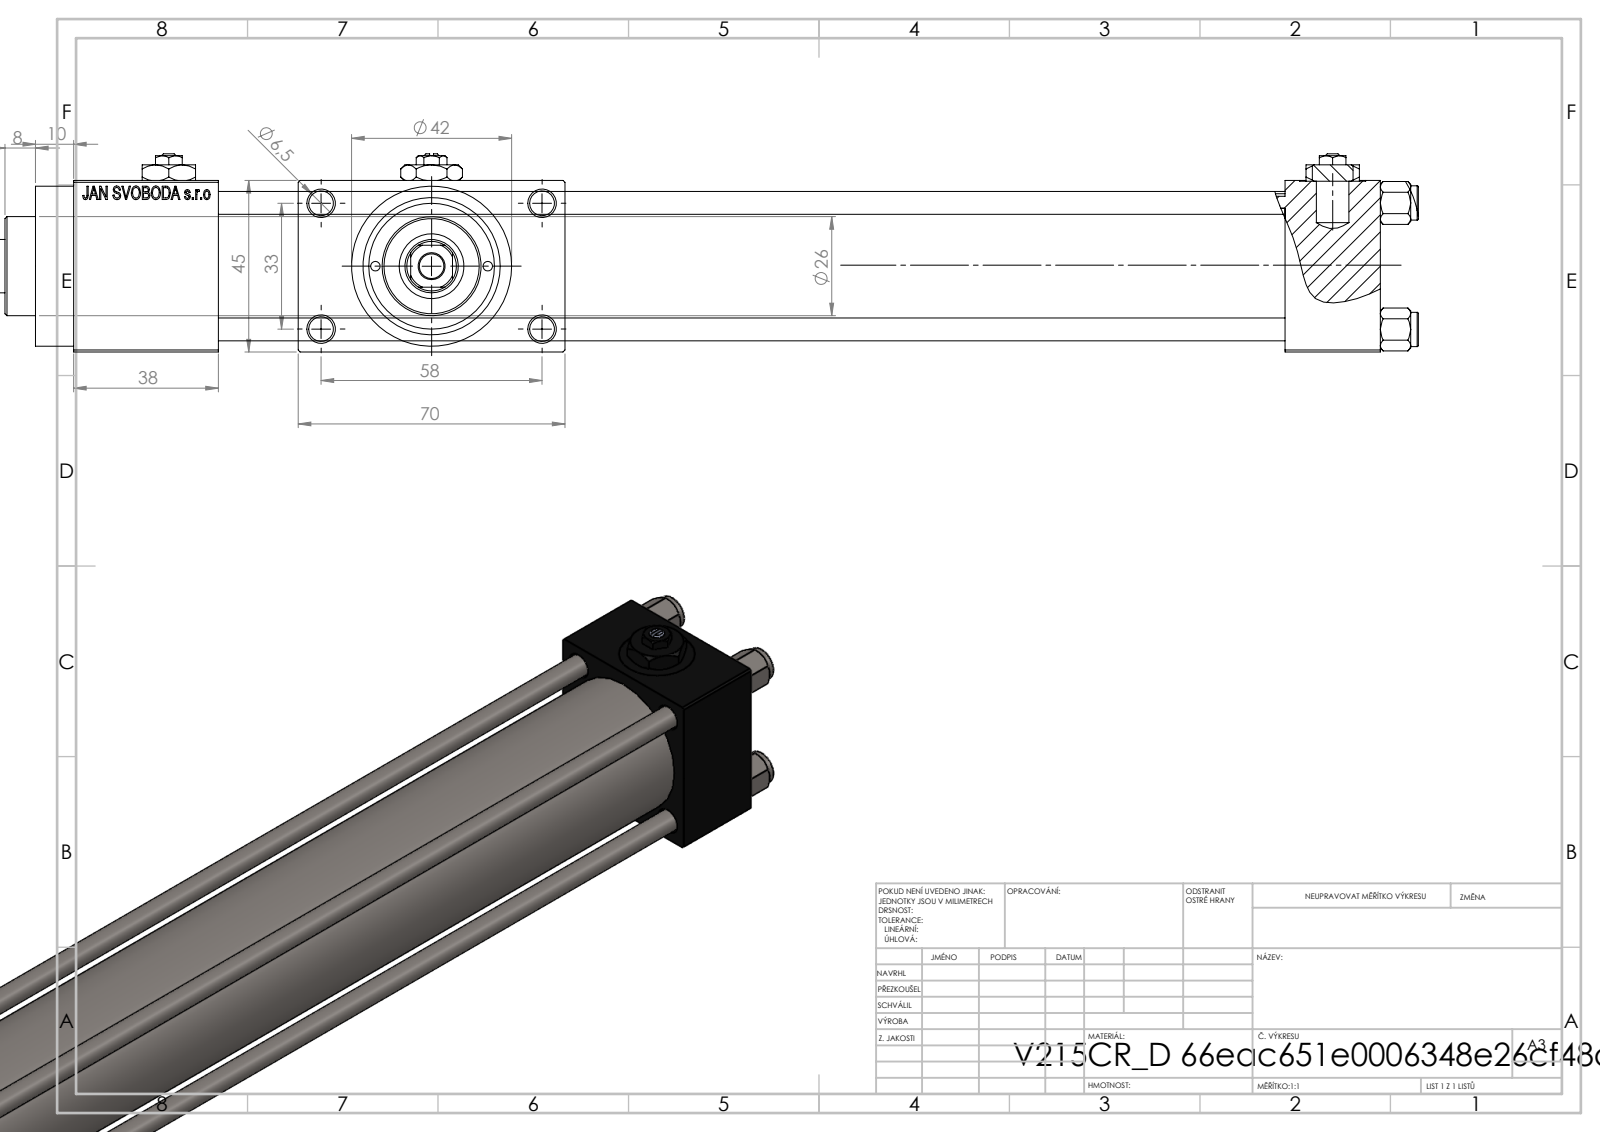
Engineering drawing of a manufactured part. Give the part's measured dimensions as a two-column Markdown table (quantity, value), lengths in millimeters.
| quantity | value |
| --- | --- |
| part name | V215CR_D_TYCINKA; V215_VC_A; V215CR_D_Body; NUT_M5_D (+2 more) |
| STEP written by | SolidWorks 2019 (CONFIG_CONTROL_DESIGN) |
| units | millimeters |
| bodies | 13 solids, 1209 faces (544 planar, 103 cylindrical, 562 other) |
| overall size | 388 × 70 × 52 |
| volume | 366 194 mm³ |
| surface area | 155 156 mm² |
| round holes (diameter × count) | 6.5 × 5, 6 × 4, 13.16 × 4, 20 × 4, 7 × 3, 2.5 × 2, 14 × 1, 17 × 1, 24 × 1, 32 × 1, 33 × 1 |
| round bosses / shafts (diameter × count) | 9 × 4, 42 × 1, 38 × 1, 26 × 1 |
| partial cylindrical surfaces (radius × count) | 6.5 × 1 |
| main face-to-face distances | 45, 25, 12.5, 280, 305, 57.5, 318, 38, 343, 70 |
| hole center spacings | 12.4, 16.7, 21.8, 23.48, 33.2, 33.37, 35.35, 35.47 |
